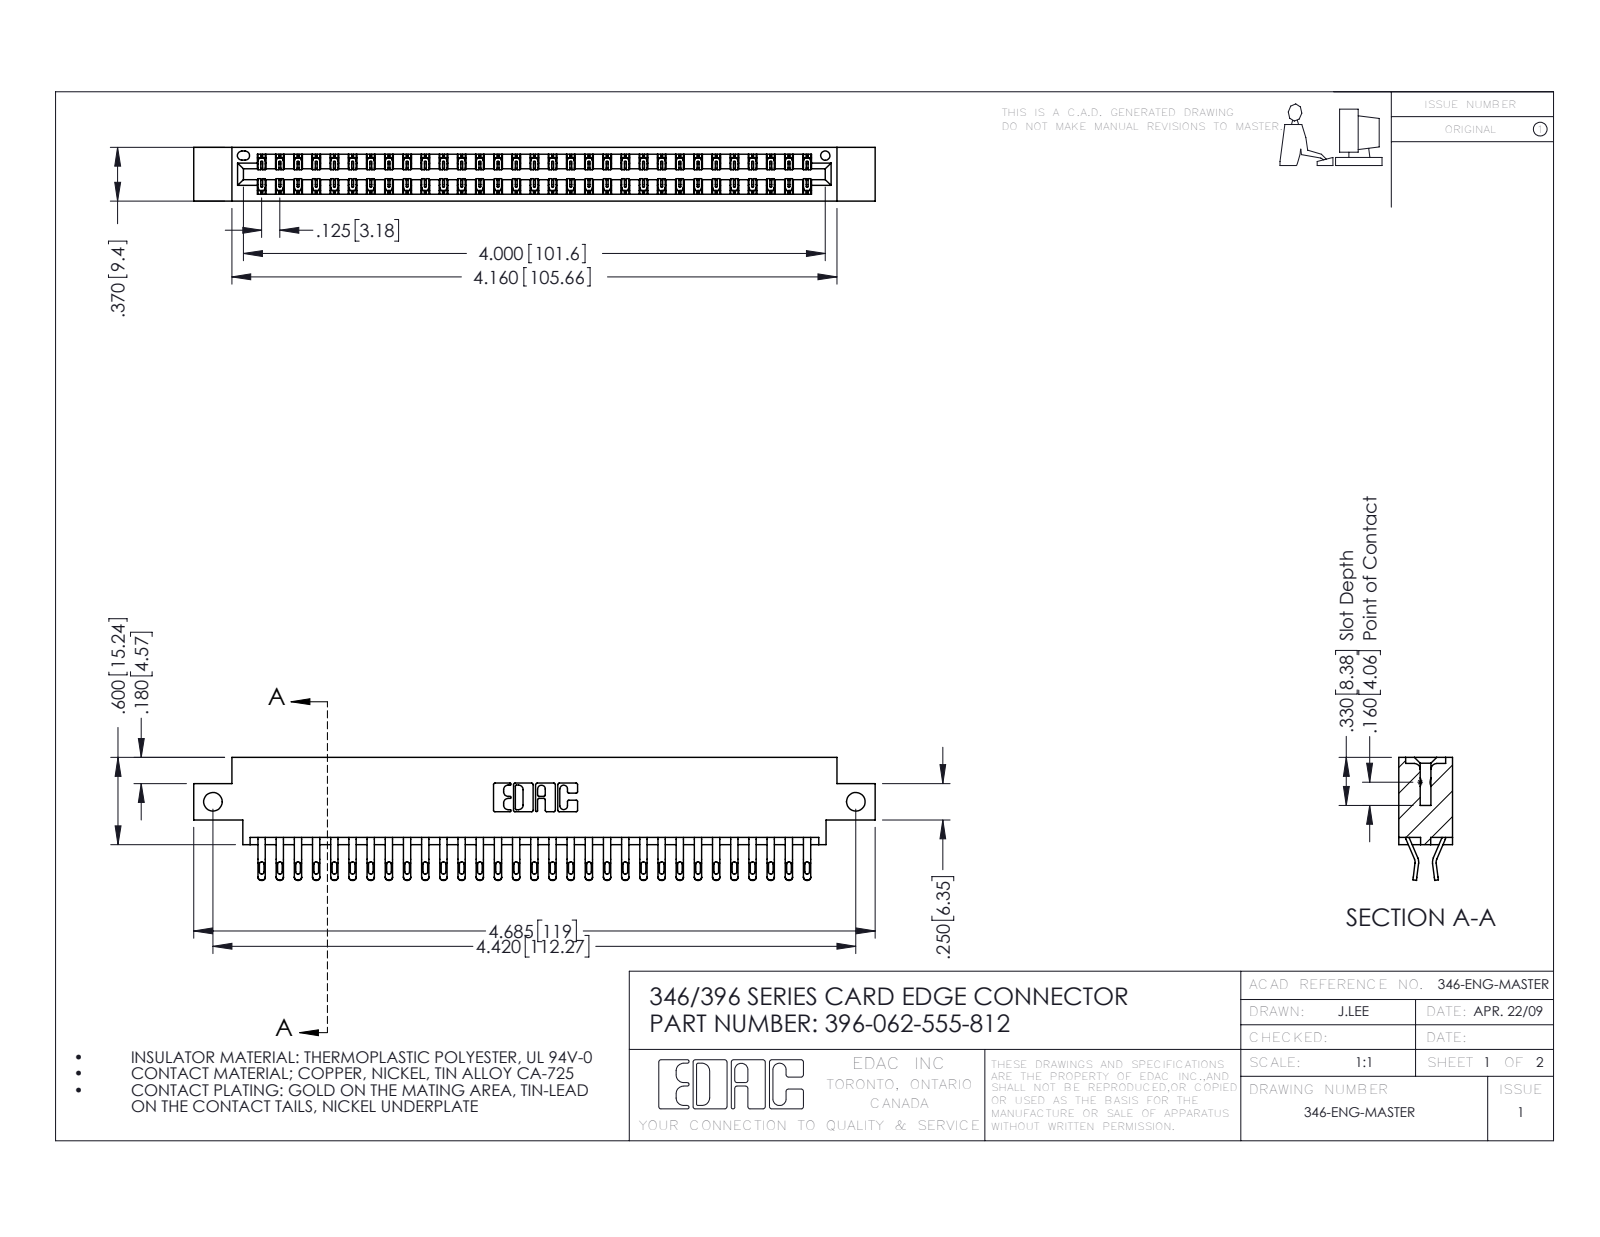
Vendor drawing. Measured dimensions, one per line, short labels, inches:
name: 346 Part_0.170 Offset - Side Mount; 396-062-555-812; 345-292-001_555 Tail
written by: SolidWorks 2016 (CONFIG_CONTROL_DESIGN)
unit: in
bodies: 63 solids, 3722 faces (2126 planar, 1596 cylindrical, 0 other)
size: 4.685 × 0.845 × 0.37
volume: 0.699 in³; area: 25.2 in²
holes: 2× ⌀0.128, 1× ⌀0.064
rounds: 124× R0.016, 124× R0.02, 93× R0.006, 22× R0.01, 6× R0.007, 6× R0.031, 3× R0.026, 2× R0.01
face distances: 0.048, 0.322, 0.37, 0.25, 0.025, 0.072, 0.298, 0.275, 0.148, 0.222
hole spacings: 4.42
